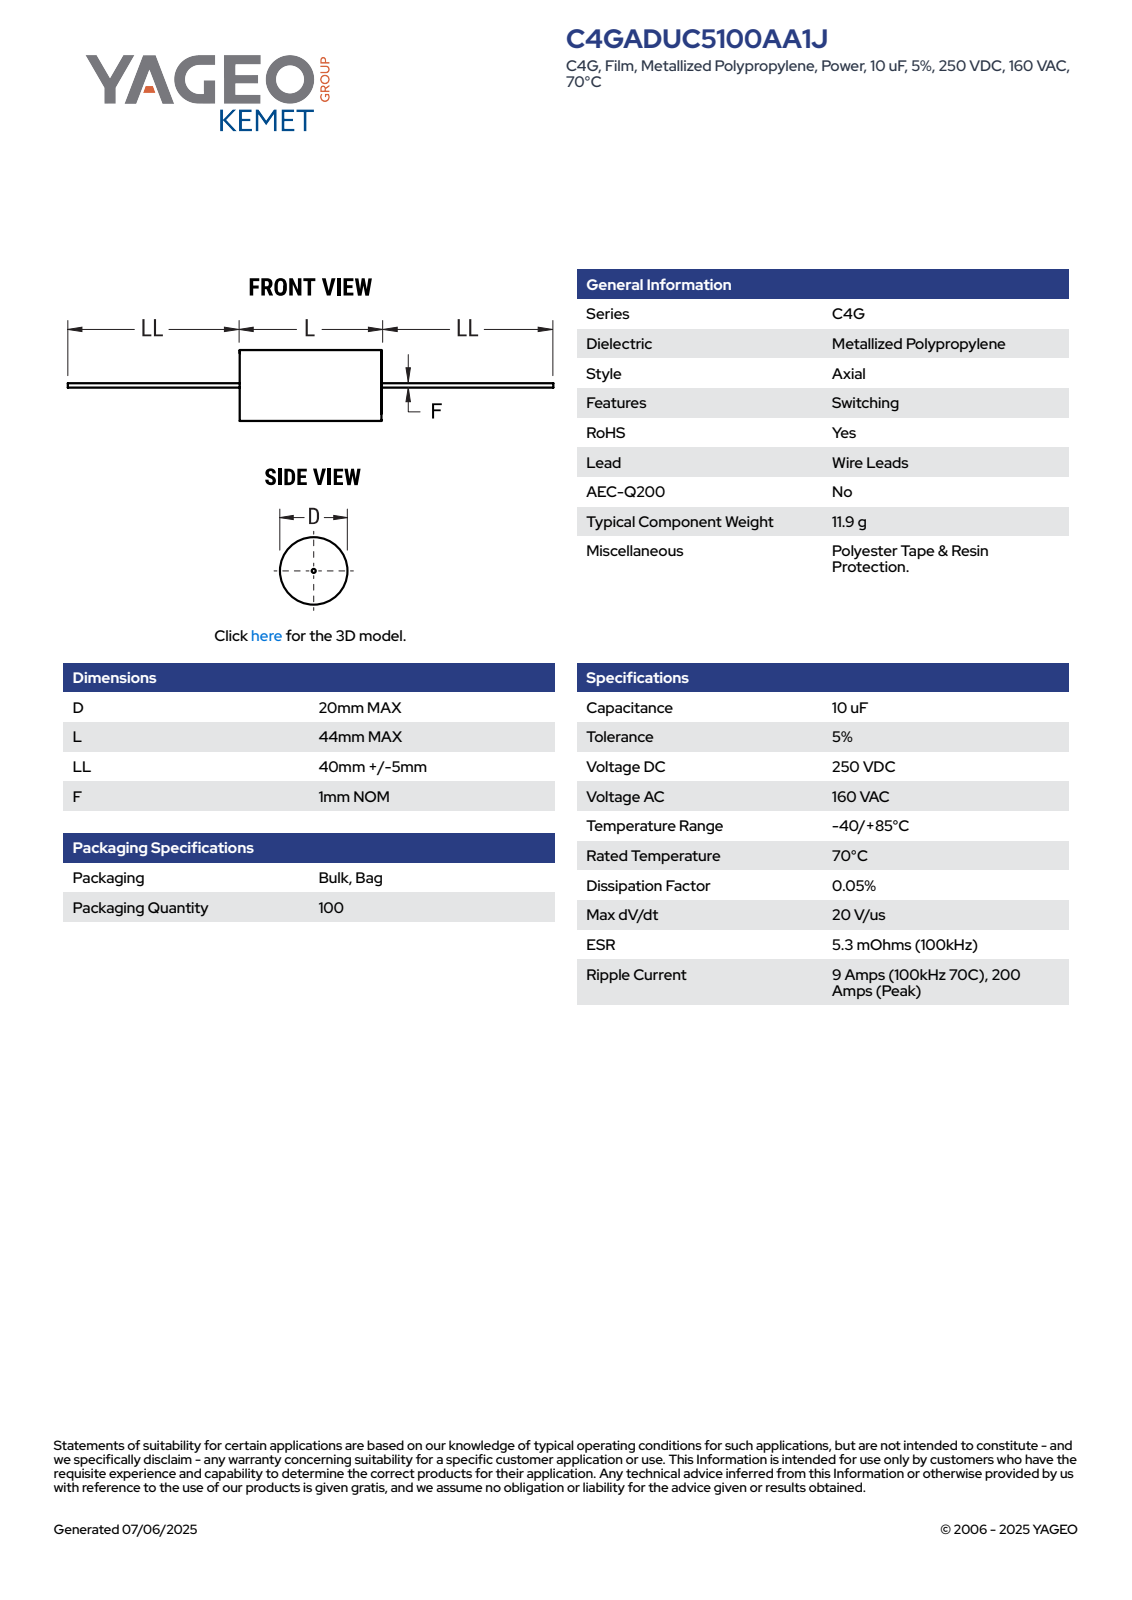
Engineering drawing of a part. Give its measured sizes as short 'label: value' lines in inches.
name: CFP_ACWF_20X44_D20L44LL45F1
written by: SolidWorks 2014 (AUTOMOTIVE_DESIGN)
unit: in
bodies: 2 solids, 87 faces (28 planar, 28 cylindrical, 31 other)
size: 5.276 × 0.787 × 0.787
volume: 0.848 in³; area: 6.67 in²
bosses: 1× ⌀0.787, 1× ⌀0.039
rounds: 1× R0.393
face distances: 1.732, 1.732, 1.771, 1.772, 3.504, 5.276, 3.504, 3.504, 1.772
